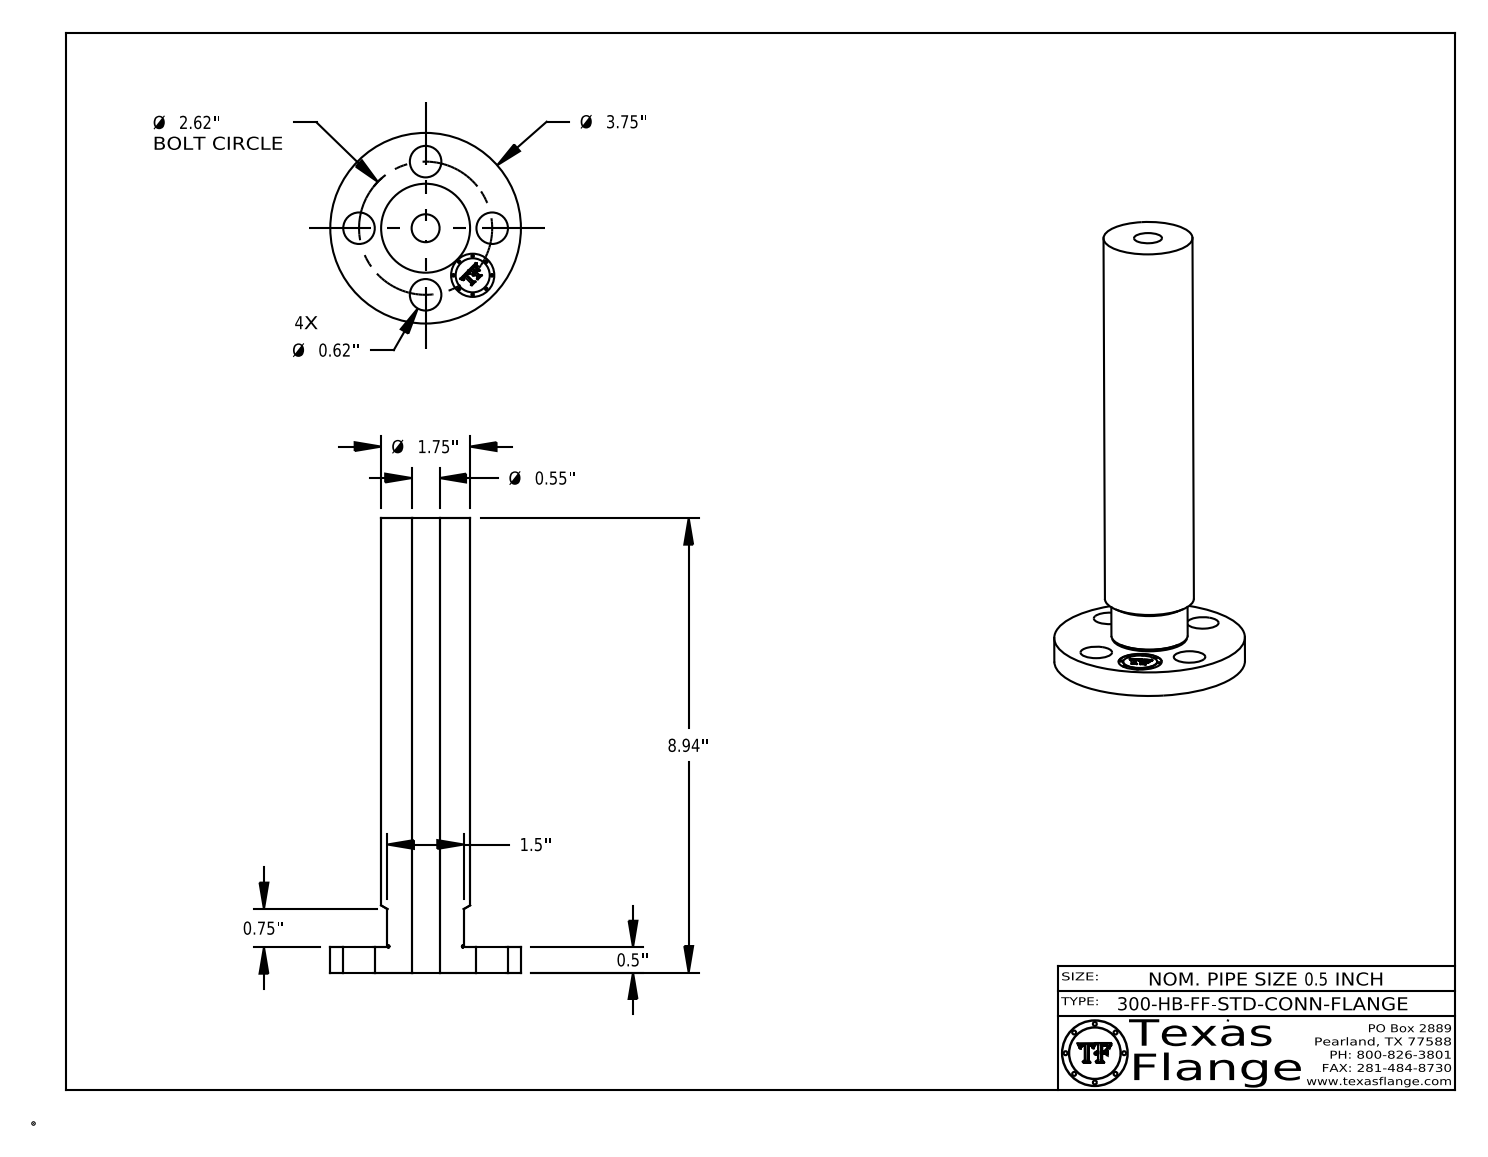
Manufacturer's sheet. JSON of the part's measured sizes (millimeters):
{"part_name": "0.5-300-HB-FF-STD-CONN-FLANGE", "step_written_by": "CATIA V5 STEP AP214 (AUTOMOTIVE_DESIGN)", "units": "millimeters", "bodies": {"solids": 1, "faces": 410, "planar": 368, "cylindrical": 36, "other": 6}, "overall_size": [227, 95.3, 95.3], "volume_mm3": 369700, "surface_area_mm2": 58970, "round_holes": [[15.7, 4], [14, 1], [21.6, 1]], "round_bosses_or_shafts": [[1.3, 8], [95.3, 1], [44.5, 1], [38.1, 1], [17, 1]], "face_to_face_distances": [12.6, 227, 214.4, 12.5, 214.5, 6.5, 6.3, 0.4, 1.2, 4.2], "hole_center_spacings": [33.3, 47, 25.5, 61.5, 66.5, 33.3]}
